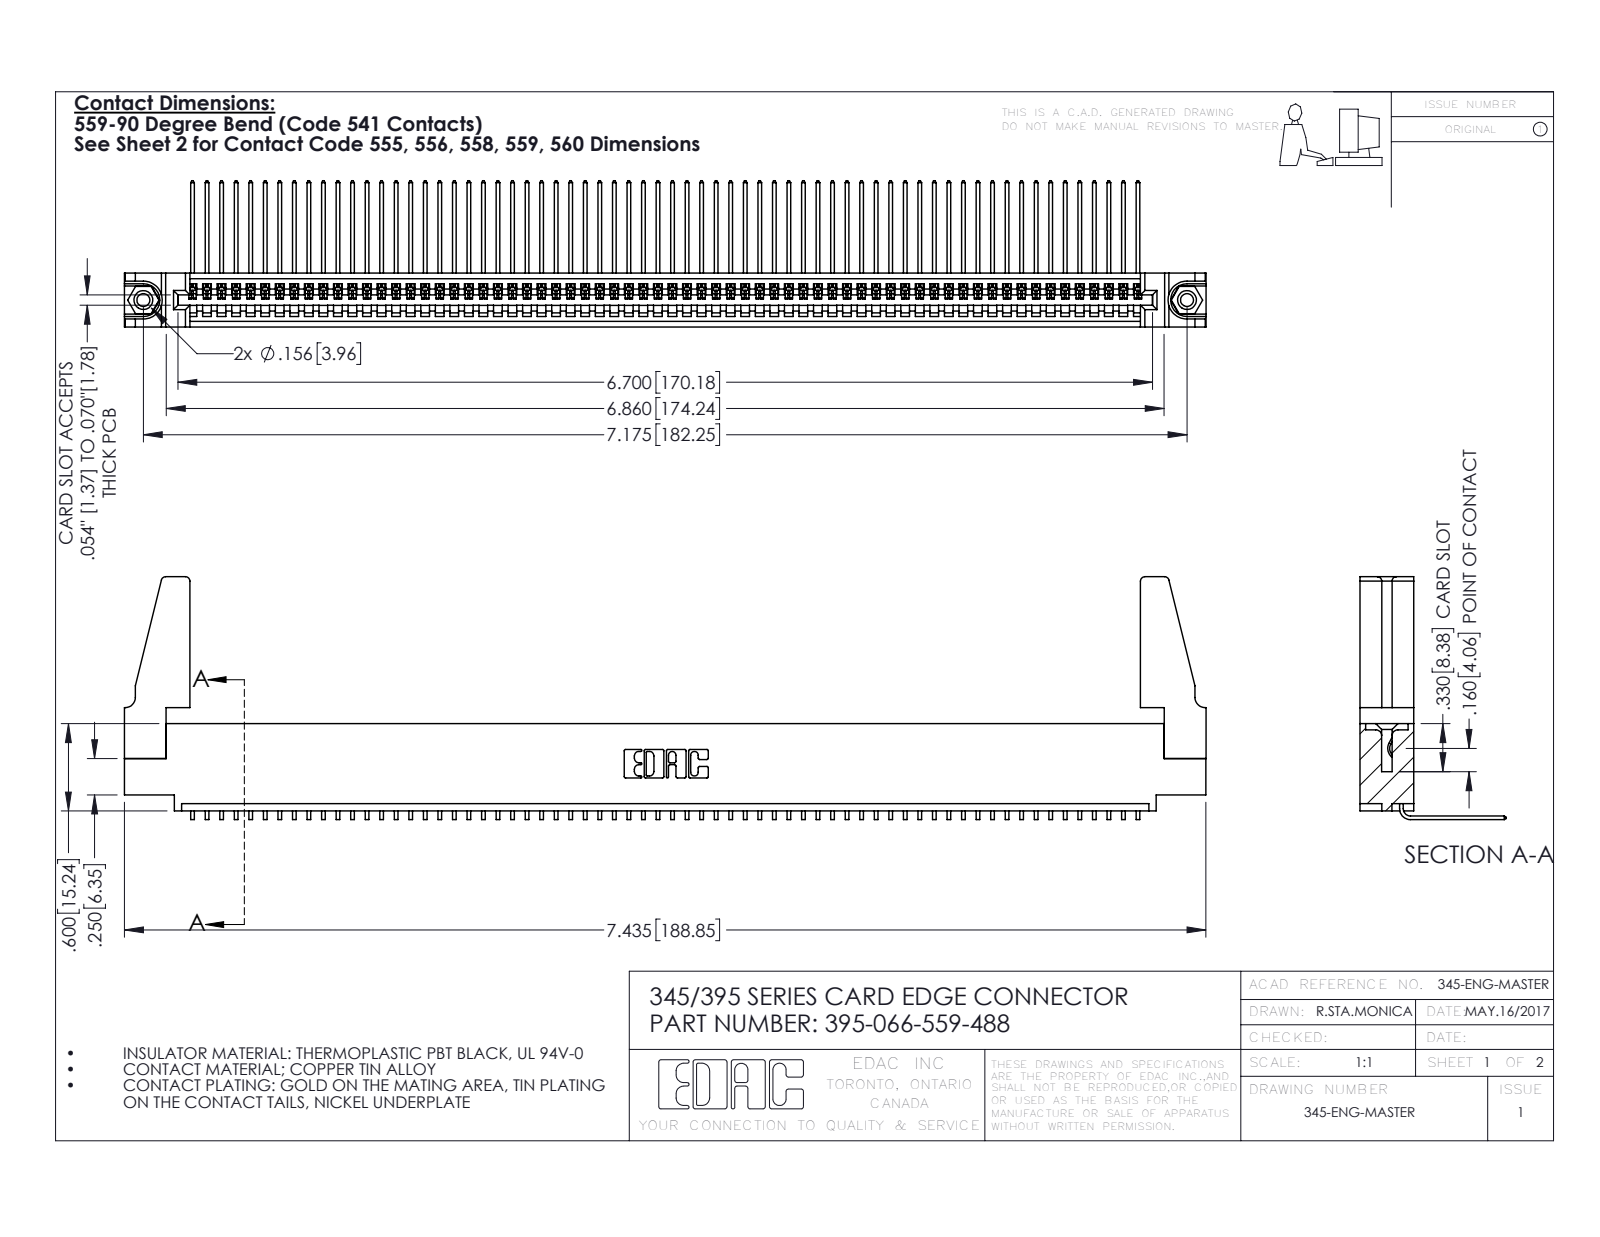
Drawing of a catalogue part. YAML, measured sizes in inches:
part_name: "345-292-001_558 559 Tail - 1; 395-066-559-488; 345-220-078_345-220-088; 345 Part_0.110 Offset - 0.156 Dia-TH (+1 more)"
step_written_by: "SolidWorks 2016 (CONFIG_CONTROL_DESIGN)"
units: inches
bodies: {solids: 71, faces: 4214, planar: 2928, cylindrical: 1270, other: 16}
overall_size: [7.436, 1.669, 1.005]
volume: 1.314
surface_area: 45.14
round_holes:
  - {diameter: 0.089, count: 2}
  - {diameter: 0.125, count: 2}
  - {diameter: 0.156, count: 2}
  - {diameter: 0.064, count: 1}
round_bosses_or_shafts:
  - {diameter: 0.155, count: 2}
partial_cylinders:
  - {radius: 0.006, count: 132}
  - {radius: 0.01, count: 22}
  - {radius: 0.03, count: 8}
  - {radius: 0.007, count: 6}
  - {radius: 0.031, count: 6}
  - {radius: 0.026, count: 3}
  - {radius: 0.031, count: 2}
  - {radius: 0.04, count: 2}
face_to_face_distances: [0.072, 0.298, 0.37, 0.098, 0.272, 0.025, 0.2, 0.225, 0.149, 0.072]
hole_center_spacings: [0.27, 6.939, 7.175]
